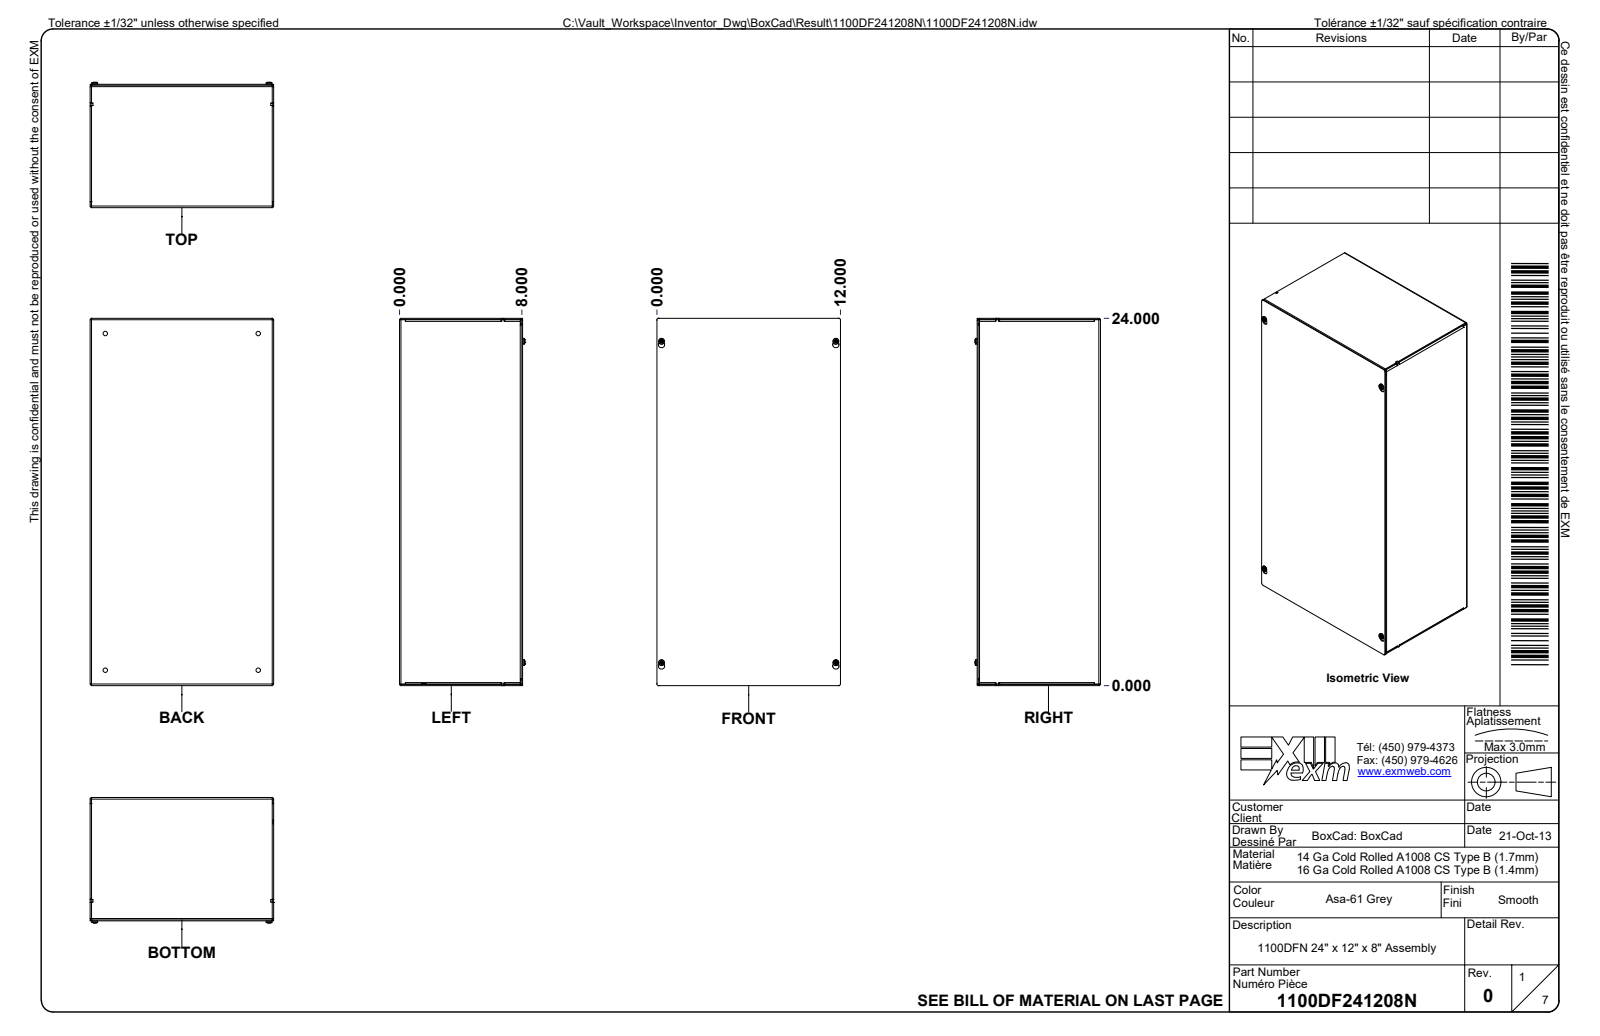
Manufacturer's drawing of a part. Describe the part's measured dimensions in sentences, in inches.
The part is named "1100DF241208N; 1100DF241208NB; 1100DF241208NB-P; 1100DF241208NC (+5 more)". Its 3-D file was written by "Autodesk Inventor 2024 (AUTOMOTIVE_DESIGN)". It is 8 solids with 3261 faces: 2018 planar, 351 cylindrical and 892 other. Overall it measures 24 by 12 by 8.183 inches. Its volume is 76.36 cubic inches and its surface area 2 392 square inches. Round holes: 4 of diameter 0.165, 4 of diameter 0.29, 4 of diameter 0.406, 2 of diameter 0.033, 2 of diameter 0.177, 1 of diameter 0.043, 1 of diameter 0.312, 1 of diameter 1.063. Round bosses or shafts: 4 of diameter 0.374, 2 of diameter 0.03, 1 of diameter 1.25, 1 of diameter 1.142, 1 of diameter 0.25, 1 of diameter 0.051. Partial cylindrical surfaces (rounded edges, fillets, slot ends): 28 of radius 0.004, 14 of radius 0.031, 14 of radius 0.099, 12 of radius 0.059, 12 of radius 0.11, 4 of radius 0.062, 4 of radius 0.094, 4 of radius 0.117. The main face-to-face distances are 0.068, 11.932, 7.932, 0.053, 8, 8.053, 7.985, 23.932, 12, 11.864. The hole center spacings are 0.222, 0.86, 10.712, 11.4, 11.402, 21, 21.511, 23.895.
